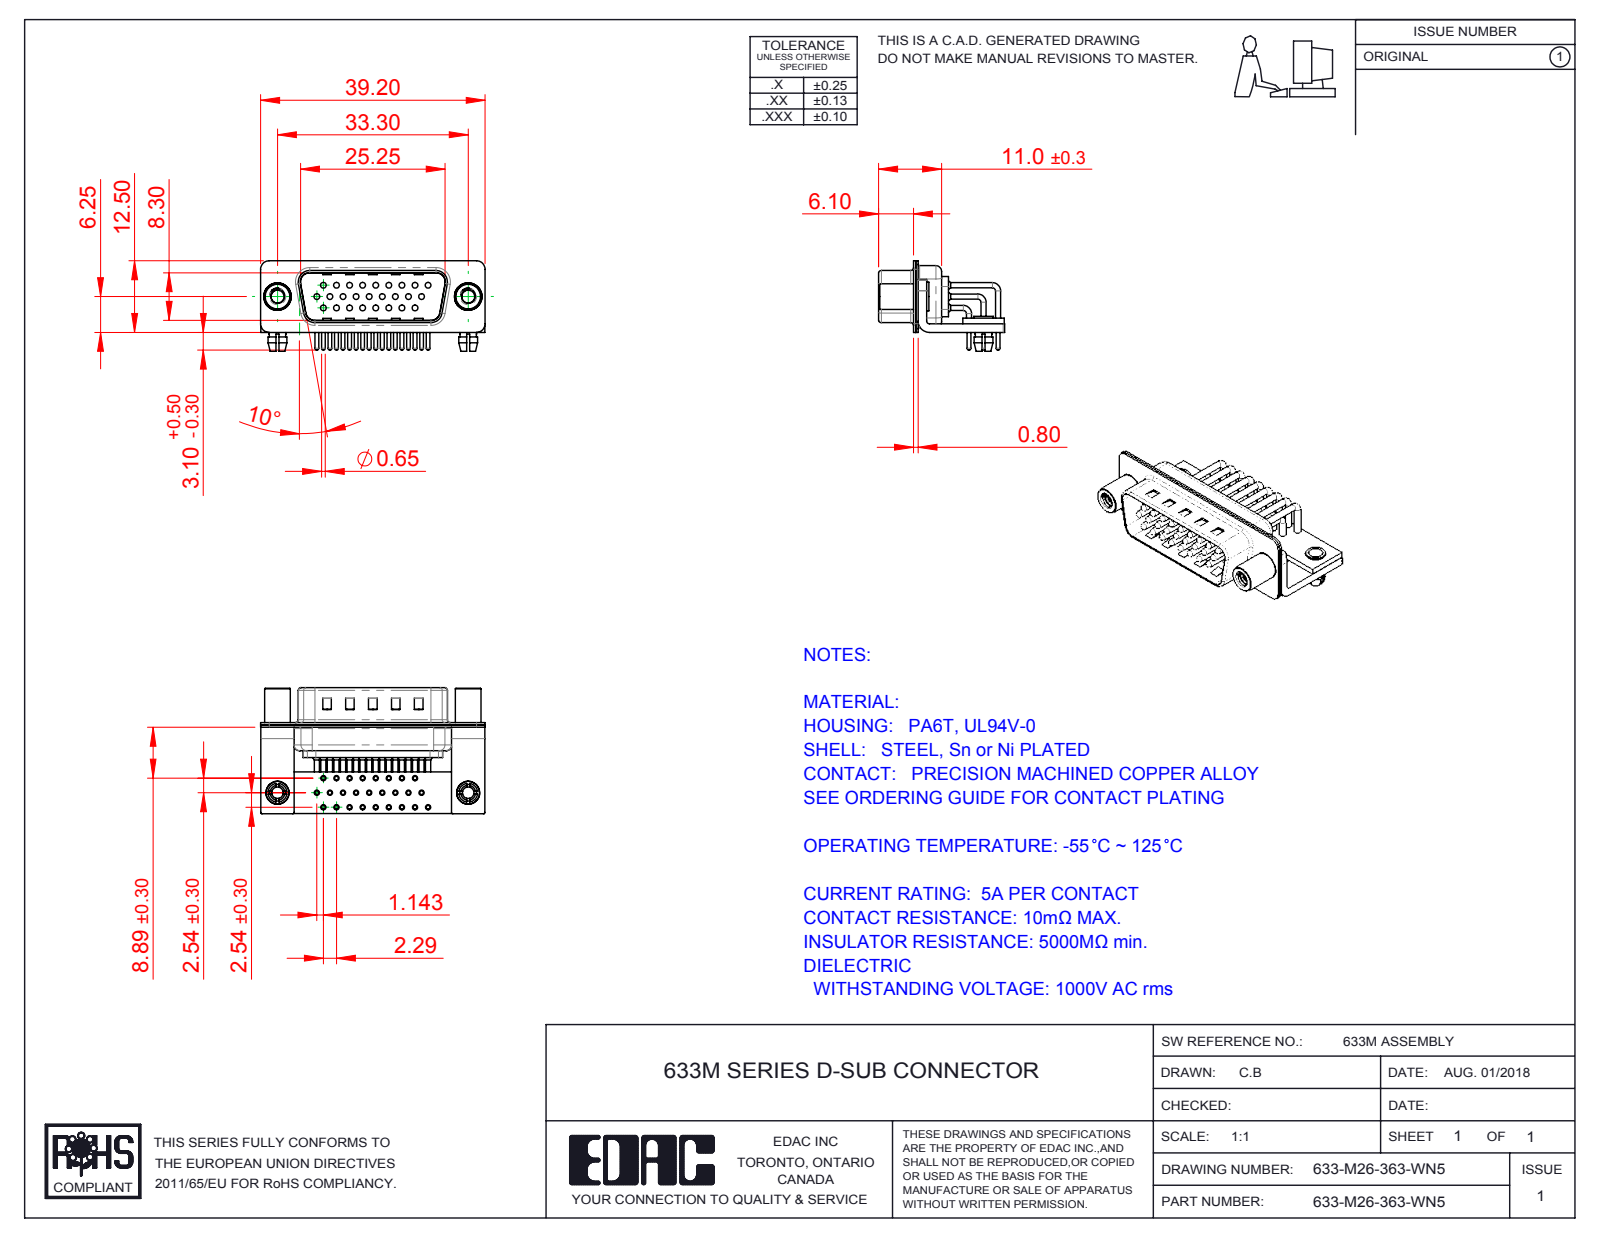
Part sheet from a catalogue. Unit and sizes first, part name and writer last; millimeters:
Units: millimetres
Overall size (bounding box): 39.2 × 22 × 15.8
Round holes (diameter × count): ⌀2 ×28, ⌀0.9 ×26, ⌀1 ×26, ⌀1.7 ×26, ⌀2.26 ×2, ⌀2.5 ×2, ⌀3.2 ×2, ⌀4 ×2, ⌀4.8 ×2
Round bosses / shafts (diameter × count): ⌀1.5 ×26, ⌀0.9 ×26, ⌀0.65 ×26, ⌀5 ×2, ⌀4.9 ×2, ⌀4.5 ×2, ⌀4 ×2, ⌀3.4 ×2
Partial cylindrical surfaces — rounded edges, fillets, slot ends (radius × count): R1.01 ×26, R0.25 ×16, R1.5 ×16, R2 ×13, R0.5 ×9, R1.6 ×8, R0.6 ×4, R0.65 ×4
Main face-to-face distances: 0.4, 1.5, 0.85, 0.8, 1, 1.25, 1.9, 10.4, 9.55, 2.5
Hole centre spacings: 4.57, 2.29, 2.28, 3.96, 6.86, 4.27, 6.05, 2.78
Volume: 2 794 mm³ · Surface area: 8 558 mm²
Bodies: 36 solids, 3444 faces (1879 planar, 1217 cylindrical, 348 other)
Part name (STEP PRODUCT): 633M Contact Row 2; 633M Housing_26 Contacts; 633M 4-40 Threaded Standoff; 633M Shell Rear_26 Contacts (+7 more)
STEP written by: SolidWorks 2016 (CONFIG_CONTROL_DESIGN)
